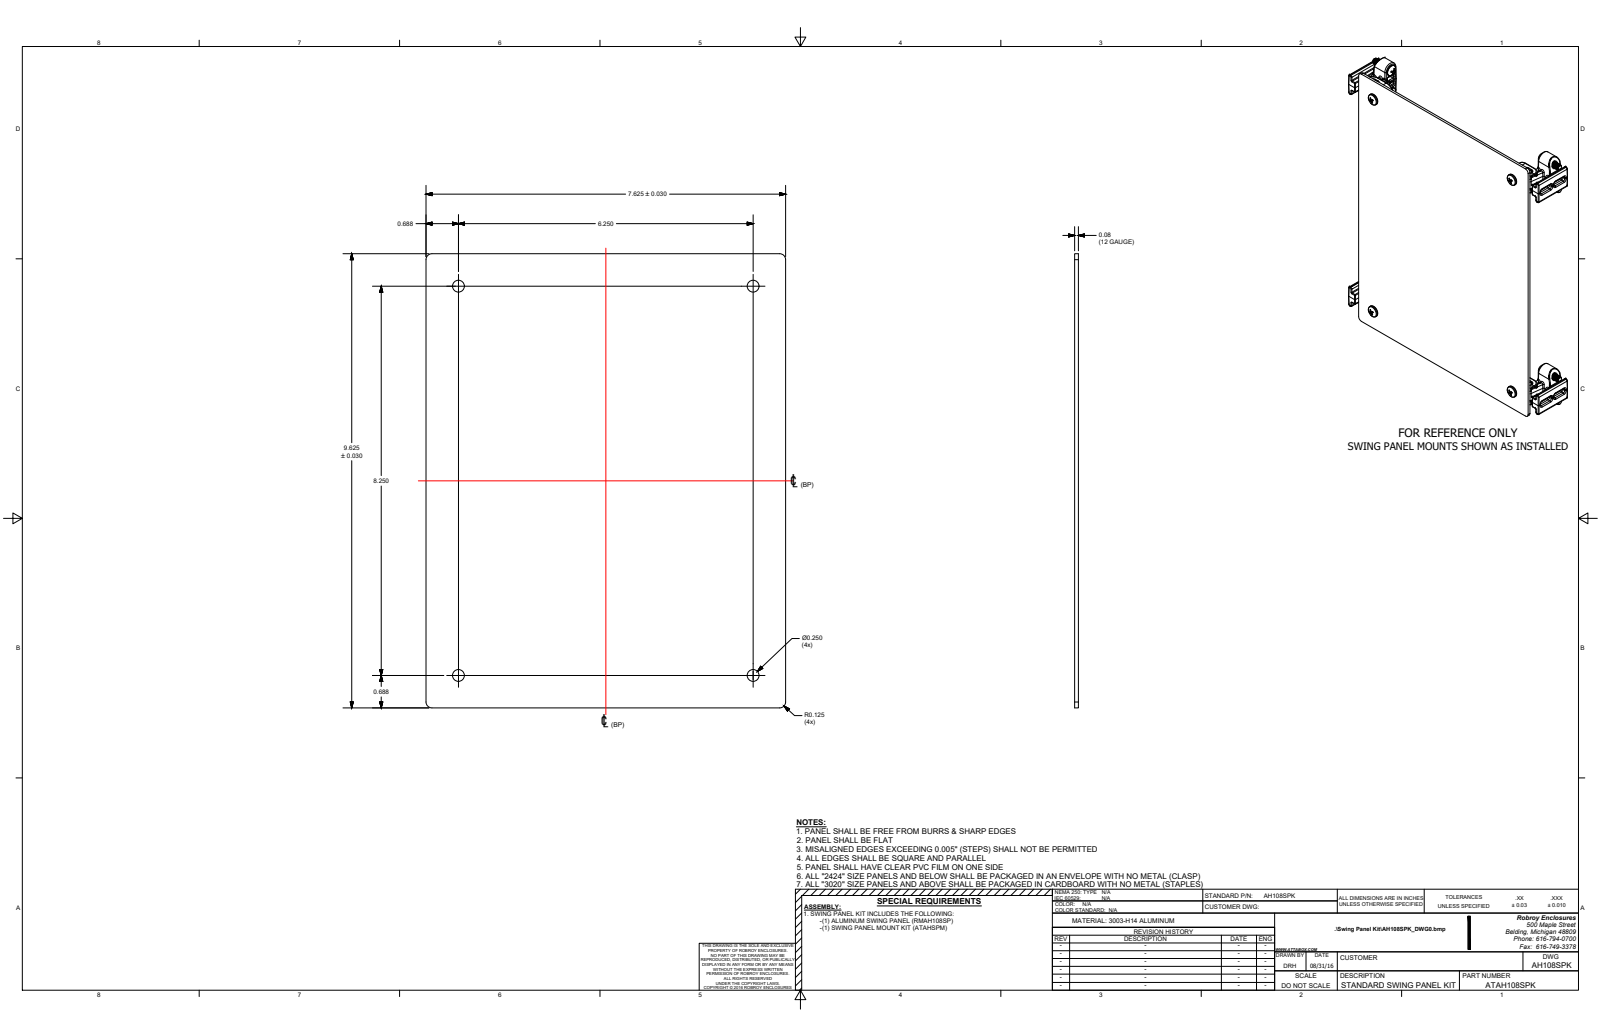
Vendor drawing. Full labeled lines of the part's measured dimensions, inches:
Part name (STEP PRODUCT): AH108SPK
STEP written by: SolidWorks 2019 (AUTOMOTIVE_DESIGN)
Units: inches
Bodies: 33 solids, 2010 faces (518 planar, 736 cylindrical, 756 other)
Overall size (bounding box): 9.625 × 8.559 × 1.448
Volume: 8.942 in³ · Surface area: 206.8 in²
Round holes (diameter × count): ⌀0.156 ×8, ⌀0.25 ×8
Round bosses / shafts (diameter × count): ⌀0.373 ×8, ⌀0.262 ×8, ⌀0.19 ×8
Partial cylindrical surfaces — rounded edges, fillets, slot ends (radius × count): R0.035 ×248, R0.02 ×124, R0.065 ×54, R0.015 ×30, R0.045 ×16, R0.05 ×16, R0.025 ×14, R0.9 ×8
Main face-to-face distances: 0.08, 0.14, 8.25, 0.5, 0.51, 0.59, 0.3, 0.36, 0.863, 8.559
Hole centre spacings: 8.25, 0.875, 6.25, 10.35, 7.375, 9.125
